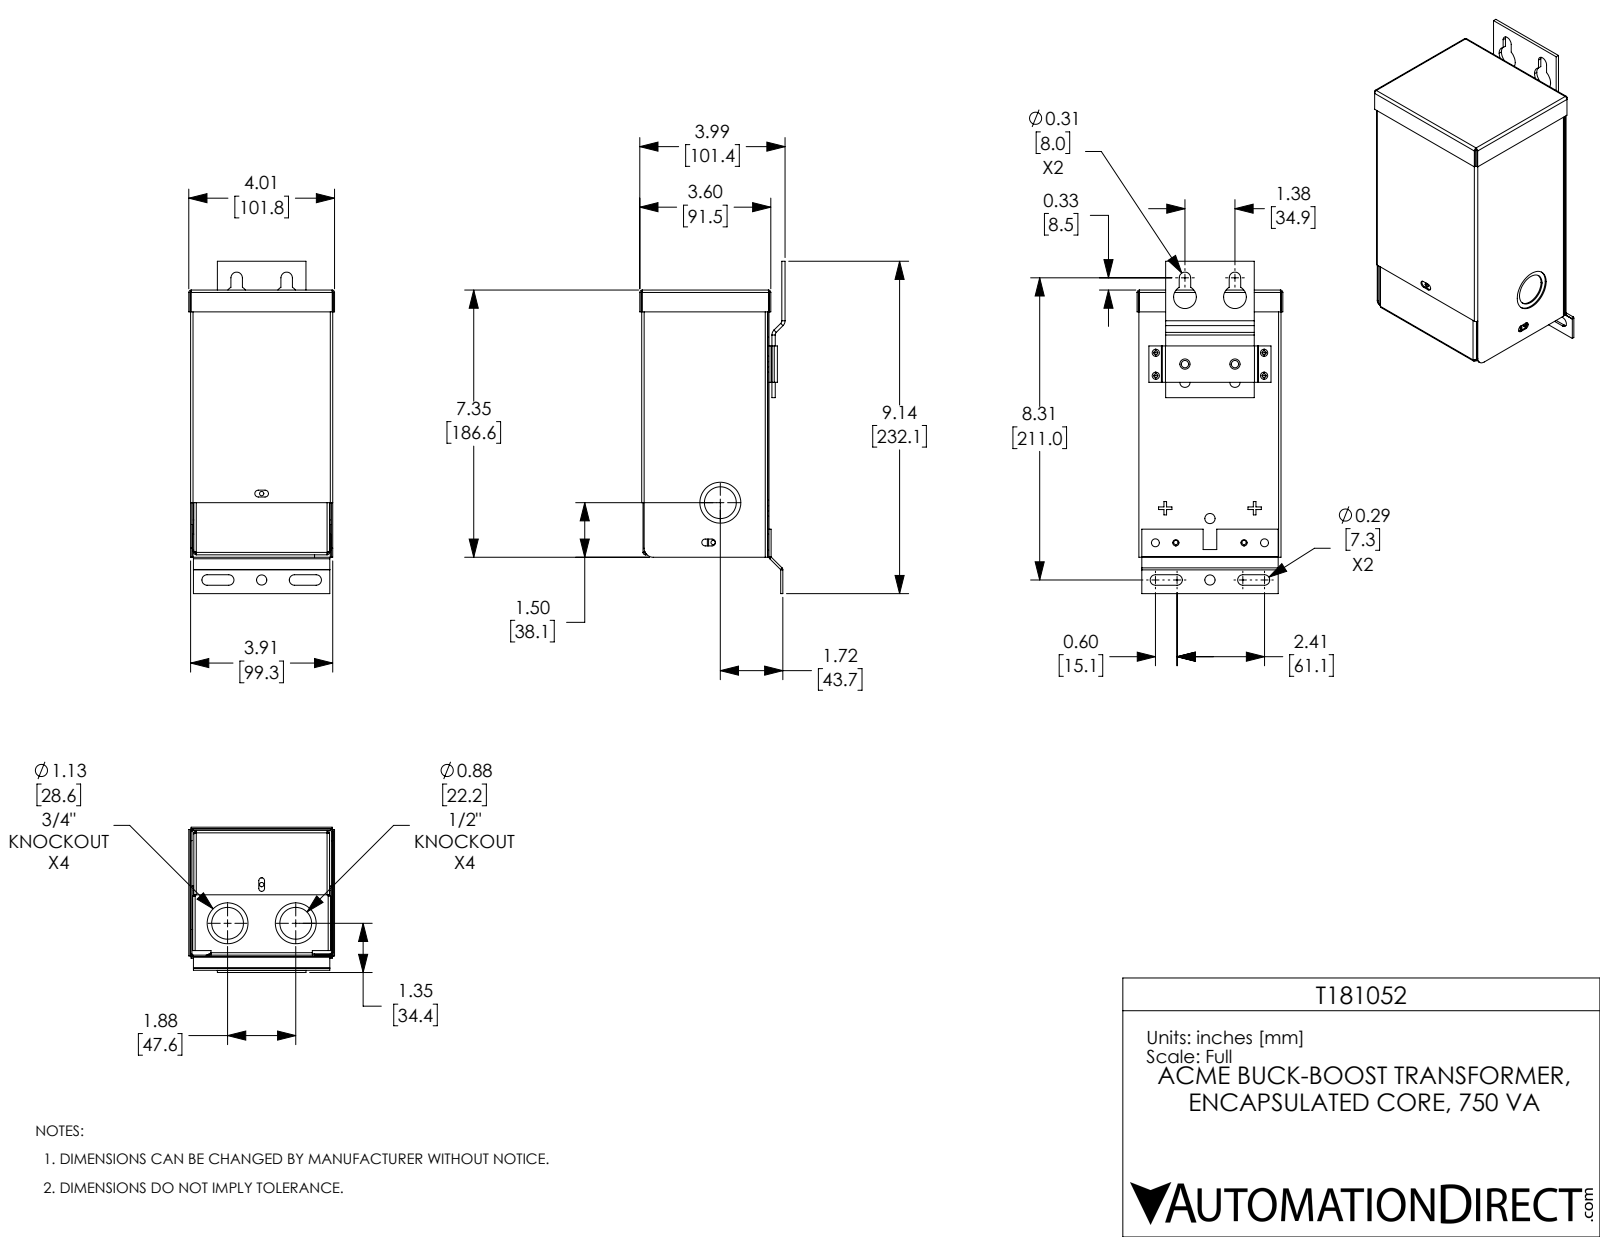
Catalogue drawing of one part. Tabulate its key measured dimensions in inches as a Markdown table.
| quantity | value |
| --- | --- |
| part name | T181052 |
| STEP written by | SolidWorks 2021 (CONFIG_CONTROL_DESIGN) |
| units | inches |
| bodies | 7 solids, 528 faces (326 planar, 154 cylindrical, 48 other) |
| overall size | 9.137 × 4.008 × 3.993 |
| volume | 6.9 in³ |
| surface area | 352.5 in² |
| round holes (diameter × count) | 0.12 × 5, 0.281 × 3, 0.281 × 3, 0.875 × 3, 1.125 × 3, 0.171 × 2, 0.187 × 2, 0.201 × 2, 0.218 × 2, 0.625 × 2, 1.125 × 1 |
| round bosses / shafts (diameter × count) | 1.197 × 3, 0.947 × 3 |
| partial cylindrical surfaces (radius × count) | 0.031 × 16, 0.067 × 16, 0.094 × 8, 0.026 × 4, 0.086 × 4, 0.144 × 4, 0.017 × 2, 0.077 × 2 |
| main face-to-face distances | 0.036, 3.464, 3.874, 3.428, 3.91, 3.839, 3.5, 0.06, 7.242, 7.182 |
| hole center spacings | 1.375, 0.5, 0.502, 0.562, 0.563, 1.145, 1.151, 1.376 |
